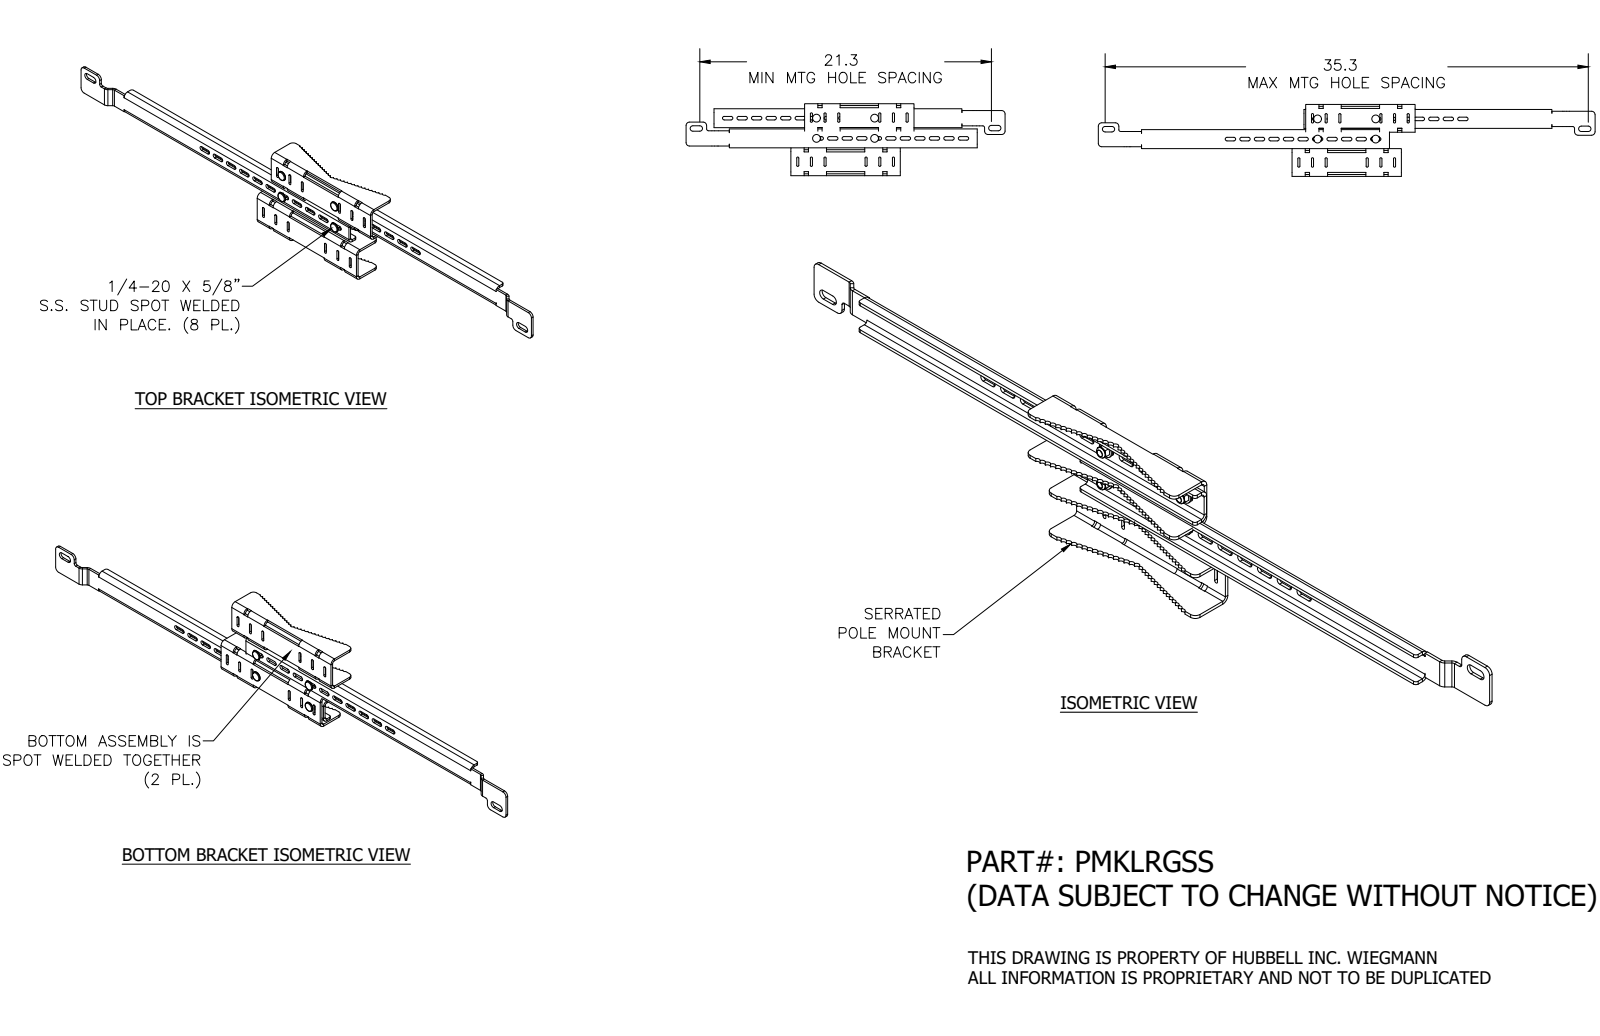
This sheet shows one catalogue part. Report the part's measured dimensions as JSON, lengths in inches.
{"part_name": "PMKLRGSS", "step_written_by": "SolidWorks 2019 (AUTOMOTIVE_DESIGN)", "units": "inches", "bodies": {"solids": 26, "faces": 2158, "planar": 632, "cylindrical": 337, "other": 1189}, "overall_size": [36.328, 17.023, 5.258], "volume_in3": 21.27, "surface_area_in2": 407.7, "round_holes": [[0.196, 4], [0.29, 4], [0.307, 2], [0.335, 1], [0.335, 1], [0.375, 1], [0.375, 1]], "round_bosses_or_shafts": [[0.563, 4], [0.435, 4], [0.25, 4], [1.075, 2], [0.625, 2], [0.625, 2], [0.562, 2], [1.125, 1]], "partial_cylinders_radius": [[0.125, 70], [0.13, 44], [0.075, 24], [0.023, 14], [0.141, 12], [0.25, 12], [0.275, 12], [0.199, 4]], "face_to_face_distances": [0.134, 0.134, 0.268, 3.227, 1.897, 1.476, 1.25, 3.361, 3.093, 1.763], "hole_center_spacings": [1.476, 4.25, 4.499, 15.306, 15.306, 15.307, 15.307, 19.552]}
